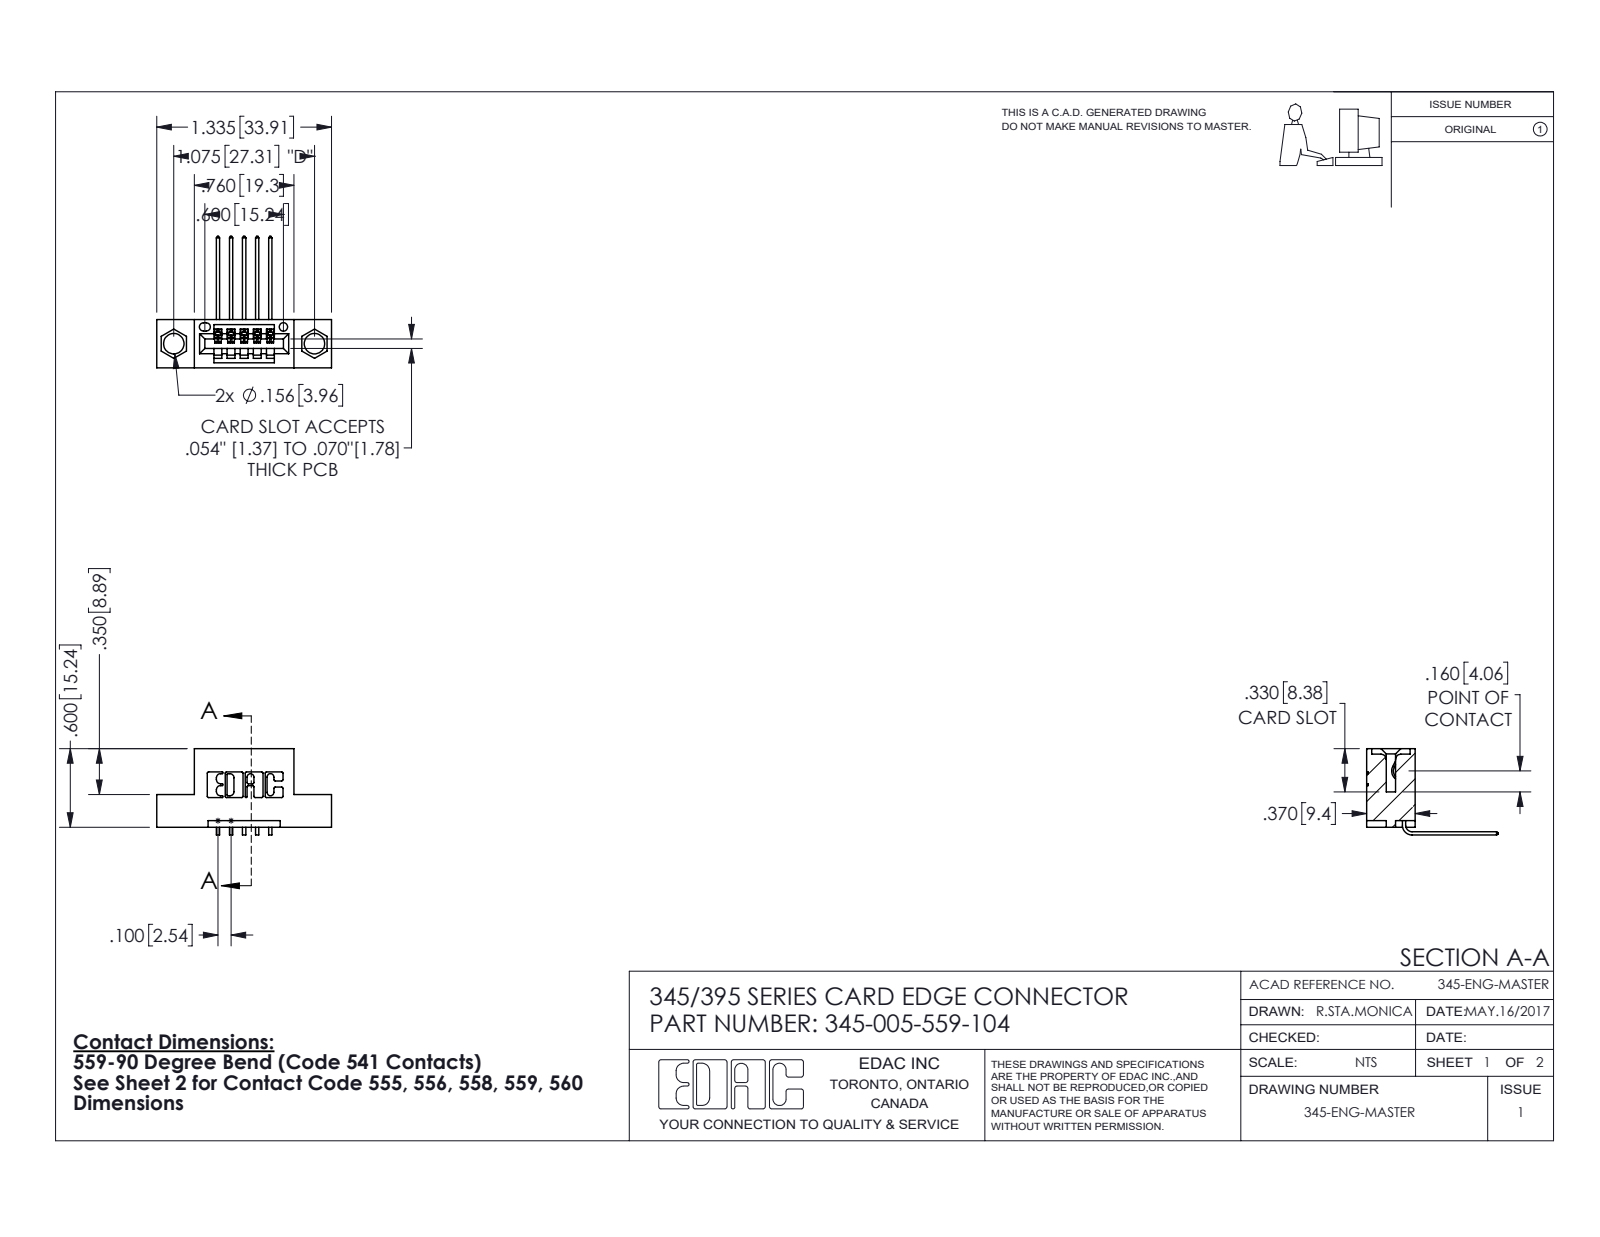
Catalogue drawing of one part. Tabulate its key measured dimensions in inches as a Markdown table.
| quantity | value |
| --- | --- |
| part name | 345 Part_Flush Mounting Lugs - 0.156 Dia-TH; 345-292-001_558 559 Tail - 1; 345-005-559-104 |
| STEP written by | SolidWorks 2016 (CONFIG_CONTROL_DESIGN) |
| units | inches |
| bodies | 6 solids, 426 faces (290 planar, 136 cylindrical, 0 other) |
| overall size | 1.335 × 1.005 × 0.659 |
| volume | 0.174 in³ |
| surface area | 4.939 in² |
| round holes (diameter × count) | 0.156 × 2, 0.064 × 1 |
| partial cylindrical surfaces (radius × count) | 0.01 × 22, 0.006 × 10, 0.007 × 6, 0.031 × 6, 0.026 × 3, 0.031 × 2, 0.04 × 2, 0.014 × 1 |
| main face-to-face distances | 0.2, 0.37, 0.1, 0.298, 0.072, 0.25, 0.06, 0.098, 0.272, 0.025 |
| hole center spacings | 0.27, 0.847, 1.075 |
